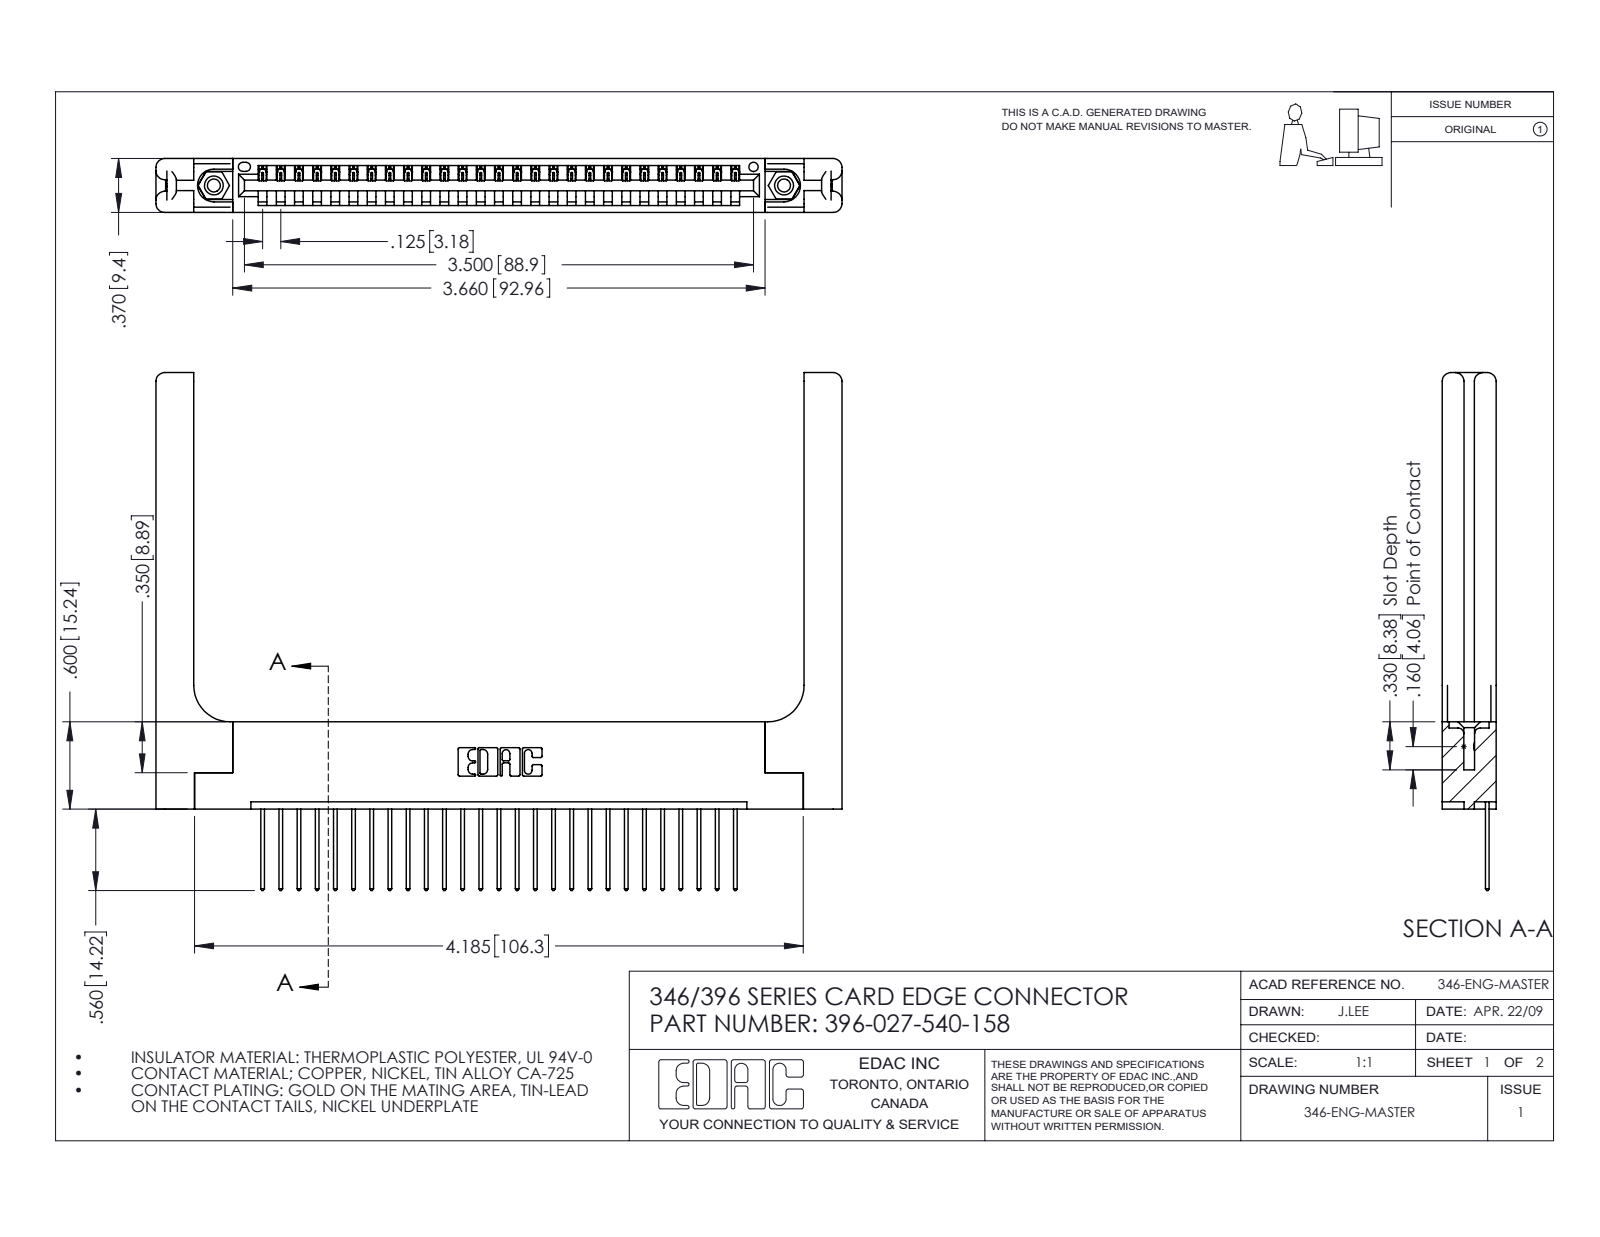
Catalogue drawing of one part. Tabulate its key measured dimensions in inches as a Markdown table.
| quantity | value |
| --- | --- |
| part name | 345-250-001_345-250-001-102; 346-220-058_345-220-058; 396-027-540-158; 346 Part_Flush Mounting Lugs - 0.156 Dia-TH (+1 more) |
| STEP written by | SolidWorks 2016 (CONFIG_CONTROL_DESIGN) |
| units | inches |
| bodies | 32 solids, 1944 faces (1304 planar, 580 cylindrical, 60 other) |
| overall size | 4.716 × 3.56 × 0.37 |
| volume | 1.154 in³ |
| surface area | 30.26 in² |
| round holes (diameter × count) | 0.089 × 2, 0.125 × 2, 0.156 × 2, 0.064 × 1 |
| round bosses / shafts (diameter × count) | 0.155 × 2 |
| partial cylindrical surfaces (radius × count) | 0.006 × 54, 0.01 × 54, 0.01 × 22, 0.06 × 16, 0.007 × 6, 0.031 × 6, 0.026 × 3, 0.03 × 2 |
| main face-to-face distances | 0.37, 0.072, 0.048, 0.322, 0.148, 0.15, 0.25, 0.298, 0.025, 0.076 |
| hole center spacings | 0.246, 3.712, 3.92 |
